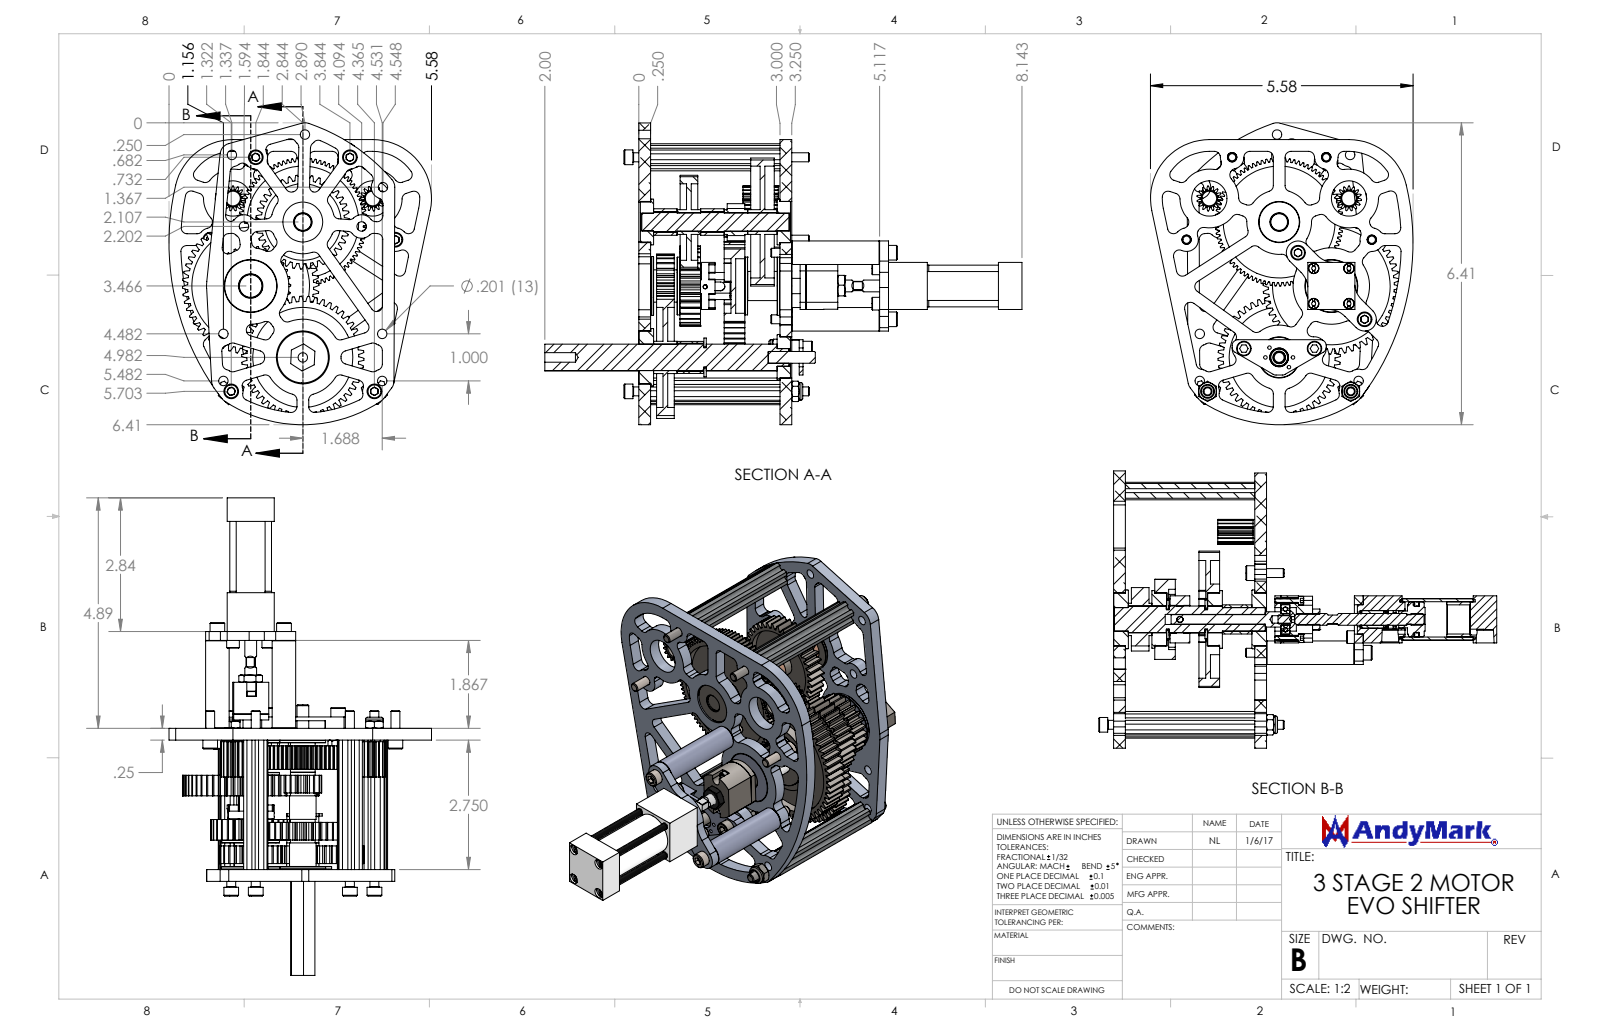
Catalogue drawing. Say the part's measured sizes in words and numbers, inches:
The part is named "60355K503_BALL BEARING_60355K503; 250x1000 dowel; .440 ID .500lg Bronze Sleeve Bearing; 500-e-klip (+8 more)". Its 3-D file was written by "SolidWorks 2014 (AUTOMOTIVE_DESIGN)". It is 96 solids with 4147 faces: 919 planar, 2687 cylindrical and 541 other. Overall it measures 11.891 by 8.79 by 6.413 inches. Its volume is 24.55 cubic inches and its surface area 413.1 square inches. Round holes: 23 of diameter 0.201, 7 of diameter 0.159, 5 of diameter 0.13, 4 of diameter 0.104, 4 of diameter 0.15, 4 of diameter 0.225, 4 of diameter 0.231, 4 of diameter 0.25, 4 of diameter 0.262, 3 of diameter 0.089, 3 of diameter 0.125, 3 of diameter 0.26. Round bosses or shafts: 9 of diameter 0.19, 8 of diameter 0.313, 7 of diameter 0.375, 5 of diameter 0.44, 4 of diameter 0.218, 4 of diameter 0.138, 4 of diameter 0.137, 3 of diameter 0.875. Partial cylindrical surfaces (rounded edges, fillets, slot ends): 171 of radius 0.125, 170 of radius 0.531, 112 of radius 0.56, 104 of radius 0.5, 76 of radius 0.38, 70 of radius 0.02, 67 of radius 0.25, 64 of radius 0.32. The main face-to-face distances are 0.25, 0.5, 3, 0.1, 2.75, 3.25, 0.619, 2.063, 1.444, 0.2. The hole center spacings are 1, 0.75, 1.132, 0.293, 2, 0.133, 0.276, 0.4.
